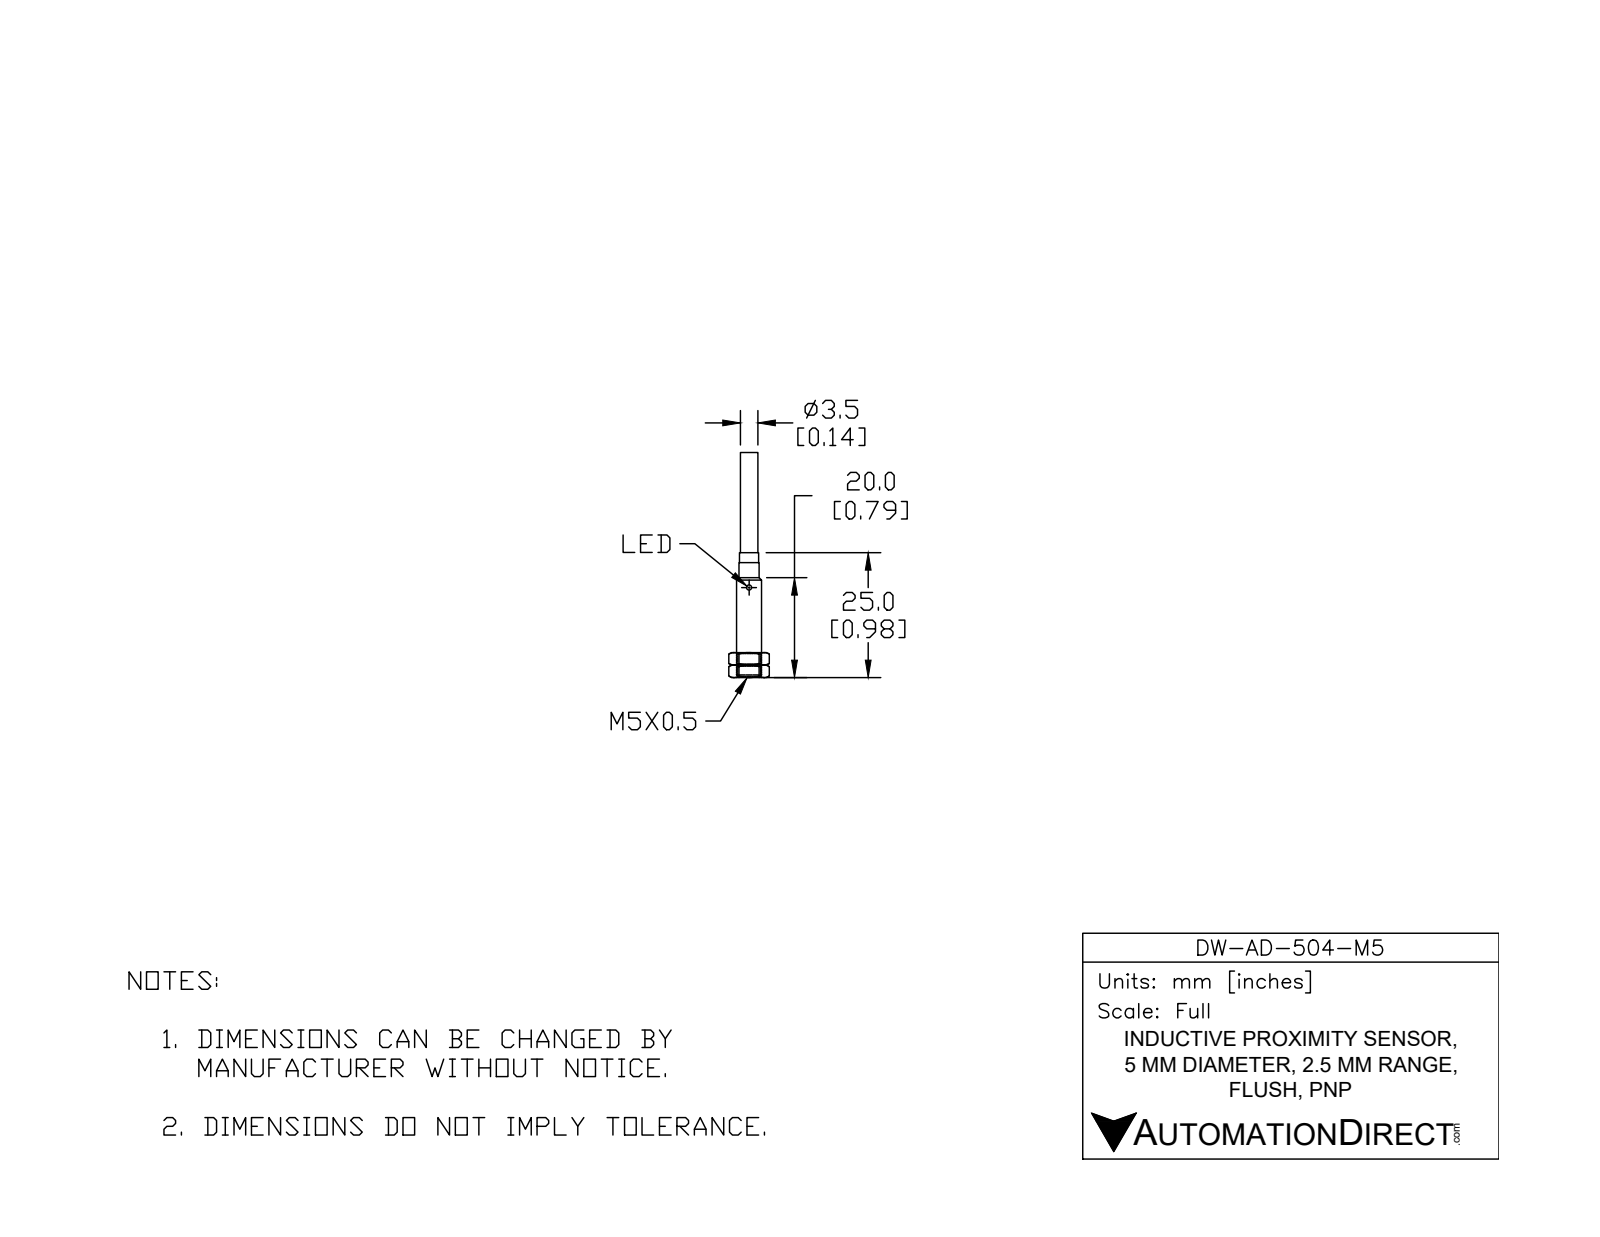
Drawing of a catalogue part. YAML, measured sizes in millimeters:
part_name: "DW-AD-504-M5"
step_written_by: "SolidWorks 2017 (AUTOMOTIVE_DESIGN)"
units: millimeters
bodies: {solids: 2, faces: 14, planar: 4, cylindrical: 6, other: 4}
overall_size: [47.9, 5, 5]
volume: 480
surface_area: 1003
round_holes:
  - {diameter: 1.5, count: 1}
  - {diameter: 3.6, count: 1}
round_bosses_or_shafts:
  - {diameter: 5, count: 1}
  - {diameter: 4.2, count: 1}
  - {diameter: 3.5, count: 1}
face_to_face_distances: [0.8, 20, 19.2, 25, 24.2, 5]
